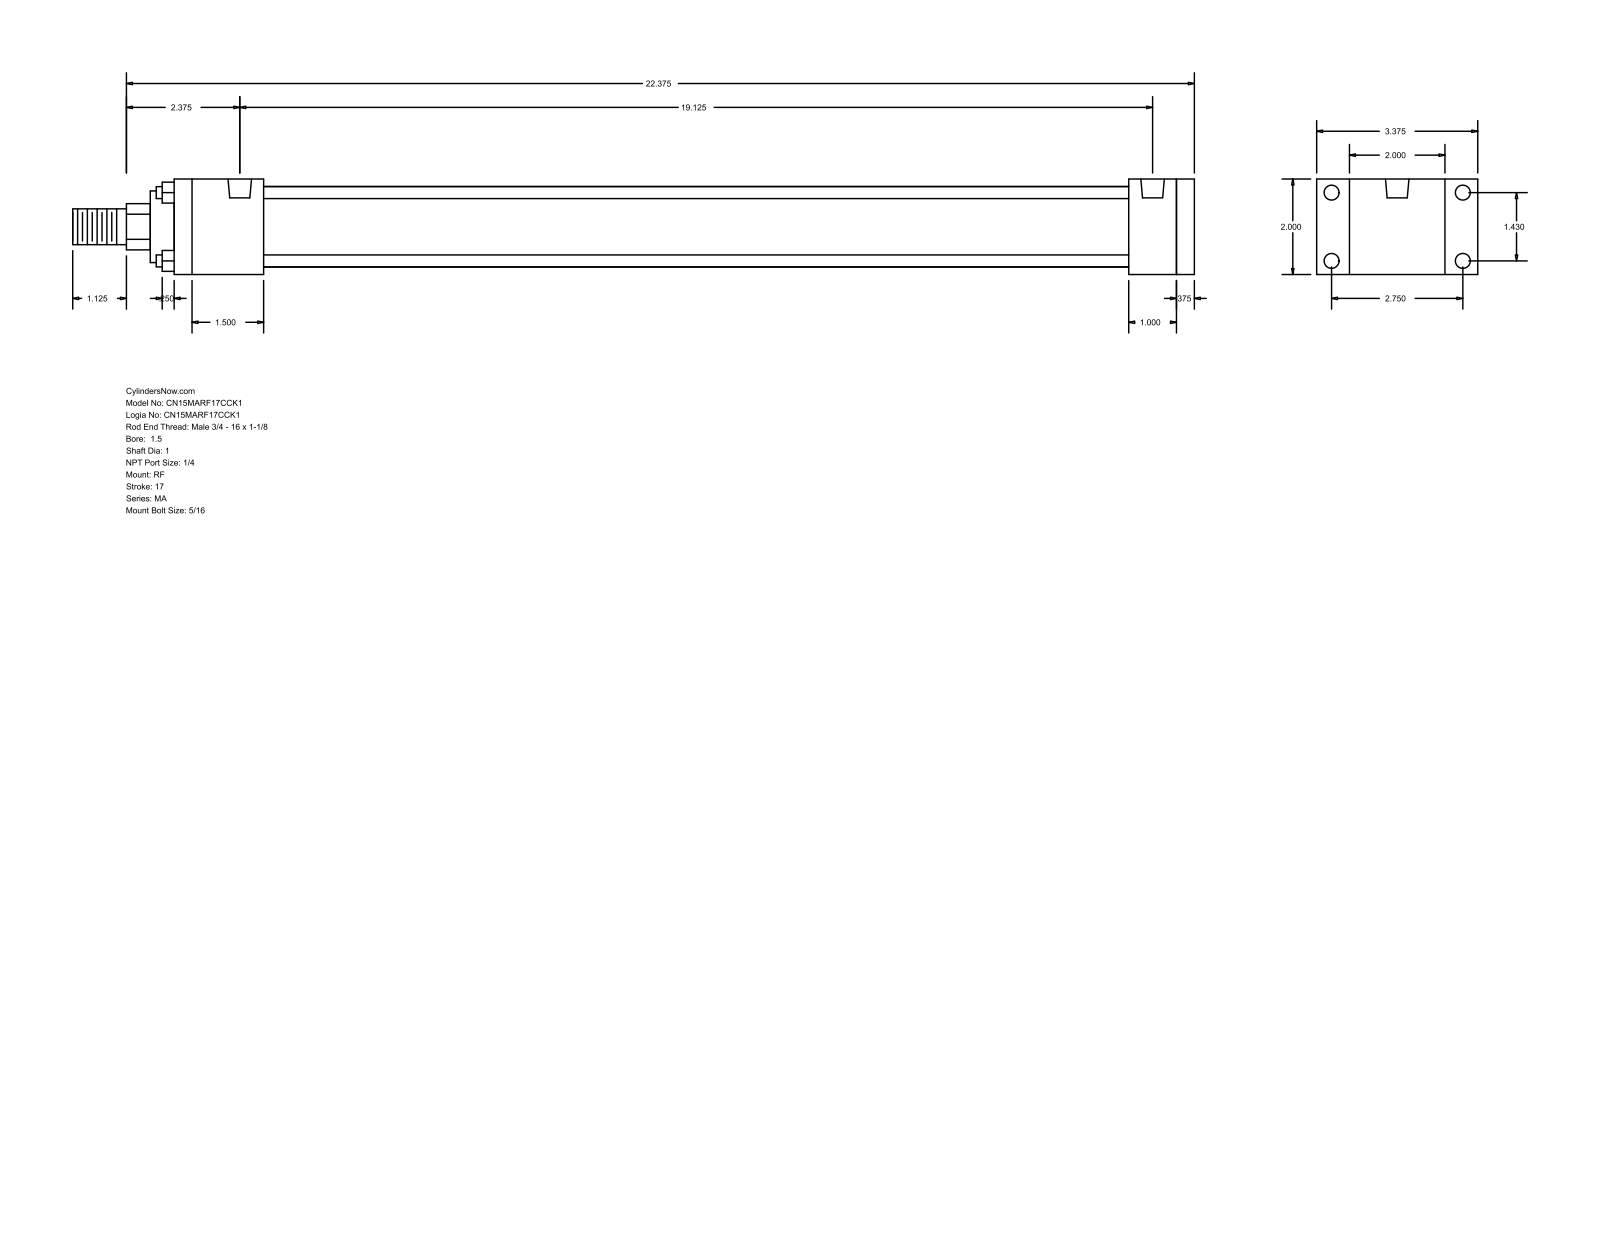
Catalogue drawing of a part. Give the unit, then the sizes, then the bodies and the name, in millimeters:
Units: millimetres
Overall size (bounding box): 596.9 × 85.72 × 50.8
Round holes (diameter × count): ⌀7.94 ×8, ⌀12.49 ×2
Round bosses / shafts (diameter × count): ⌀6.35 ×4, ⌀42.93 ×1, ⌀38.1 ×1, ⌀25.4 ×1, ⌀19.05 ×1
Partial cylindrical surfaces — rounded edges, fillets, slot ends (radius × count): R12.29 ×1
Main face-to-face distances: 50.8, 9.53, 533.4, 25.4, 542.93, 508, 34.93, 47.63, 460.37, 485.77
Hole centre spacings: 36.32, 69.84, 78.72, 485.77
Bodies: 0 solids, 92 faces (64 planar, 28 cylindrical, 0 other)
Part name (STEP PRODUCT): MA_RF__0150_1
STEP written by: GSSL Pune (CONFIG_CONTROL_DESIGN)
